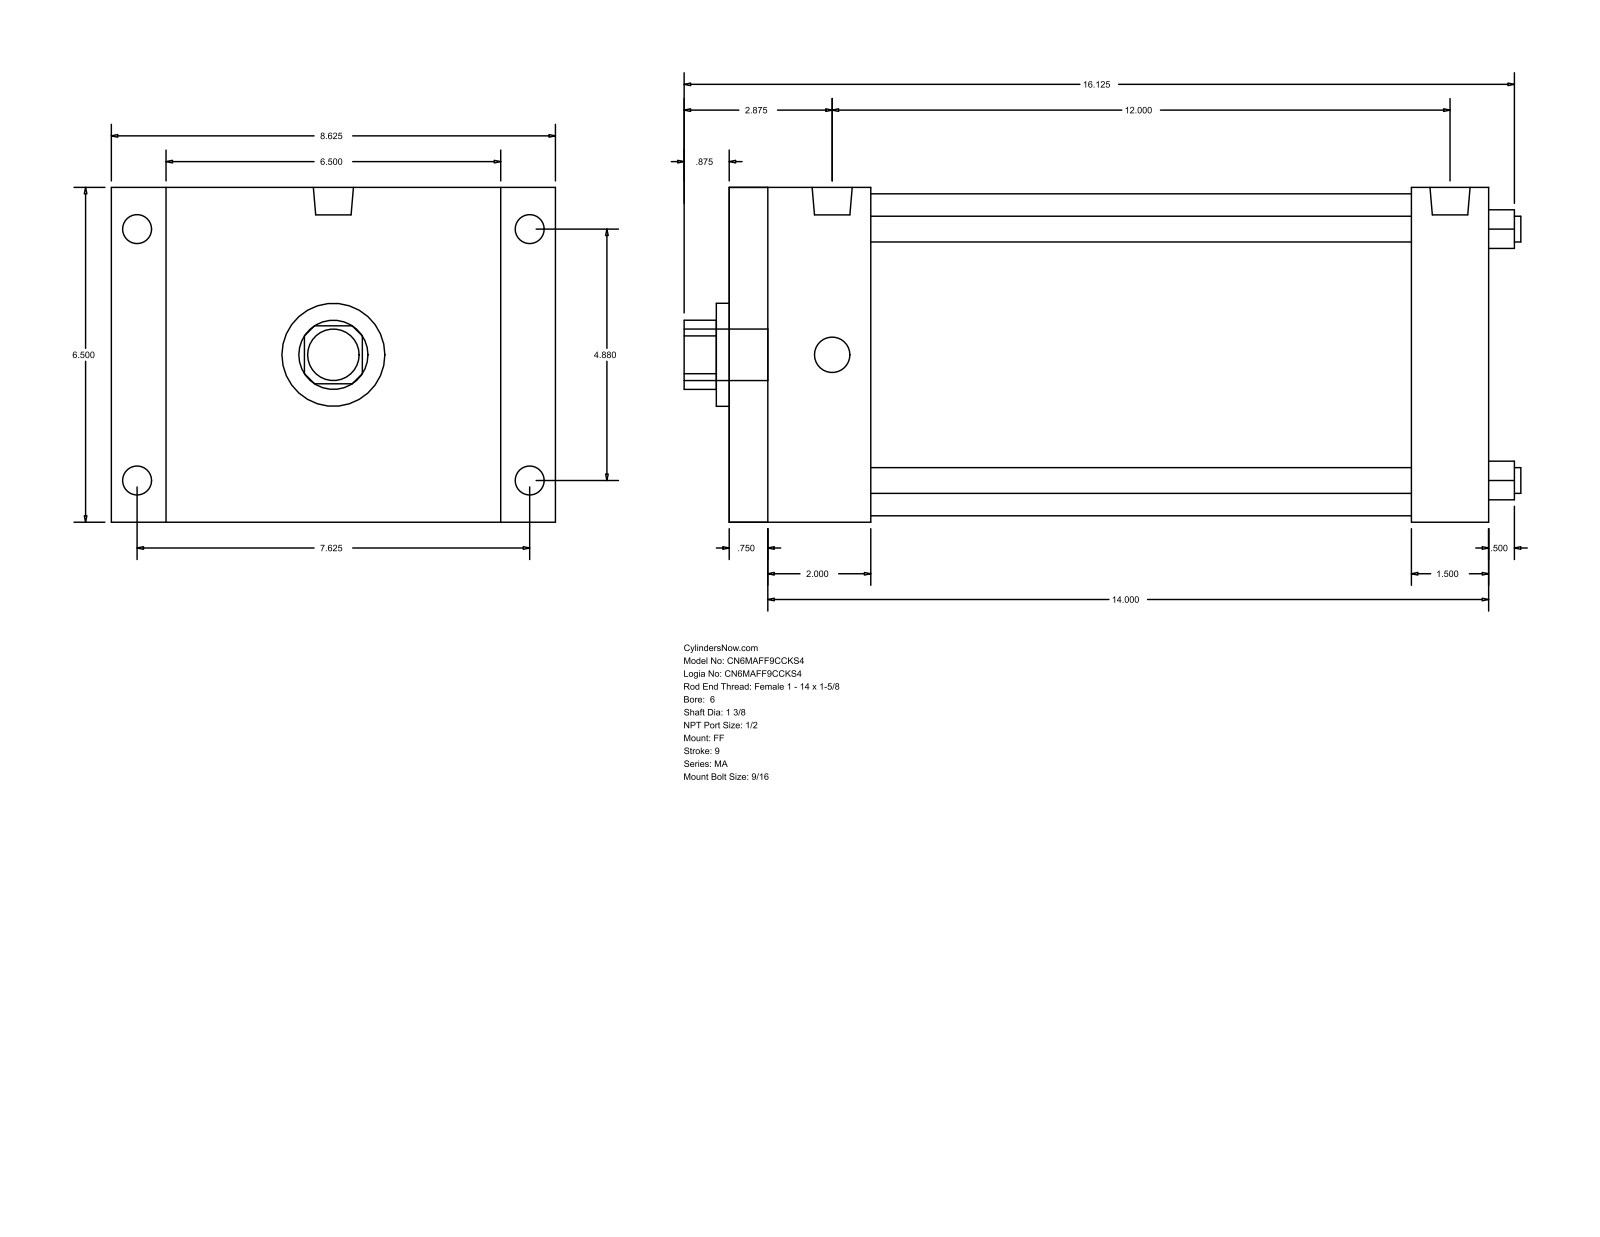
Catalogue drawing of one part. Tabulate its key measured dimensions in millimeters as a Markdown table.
| quantity | value |
| --- | --- |
| part name | MA_FF__0600_1.375 |
| STEP written by | GSSL Pune (CONFIG_CONTROL_DESIGN) |
| units | millimeters |
| bodies | 0 solids, 92 faces (64 planar, 28 cylindrical, 0 other) |
| overall size | 412.75 × 219.07 × 165.1 |
| round holes (diameter × count) | 12.7 × 4, 34.92 × 1, 50.8 × 1, 158.75 × 1 |
| round bosses / shafts (diameter × count) | 17.46 × 4, 14.29 × 4, 19.77 × 2, 25.4 × 1 |
| partial cylindrical surfaces (radius × count) | 17.06 × 1 |
| main face-to-face distances | 165.1, 374.65, 15.87, 358.78, 50.8, 320.67, 66.67, 307.98, 336.54, 269.87 |
| hole center spacings | 87.65, 123.96, 175.31 |
